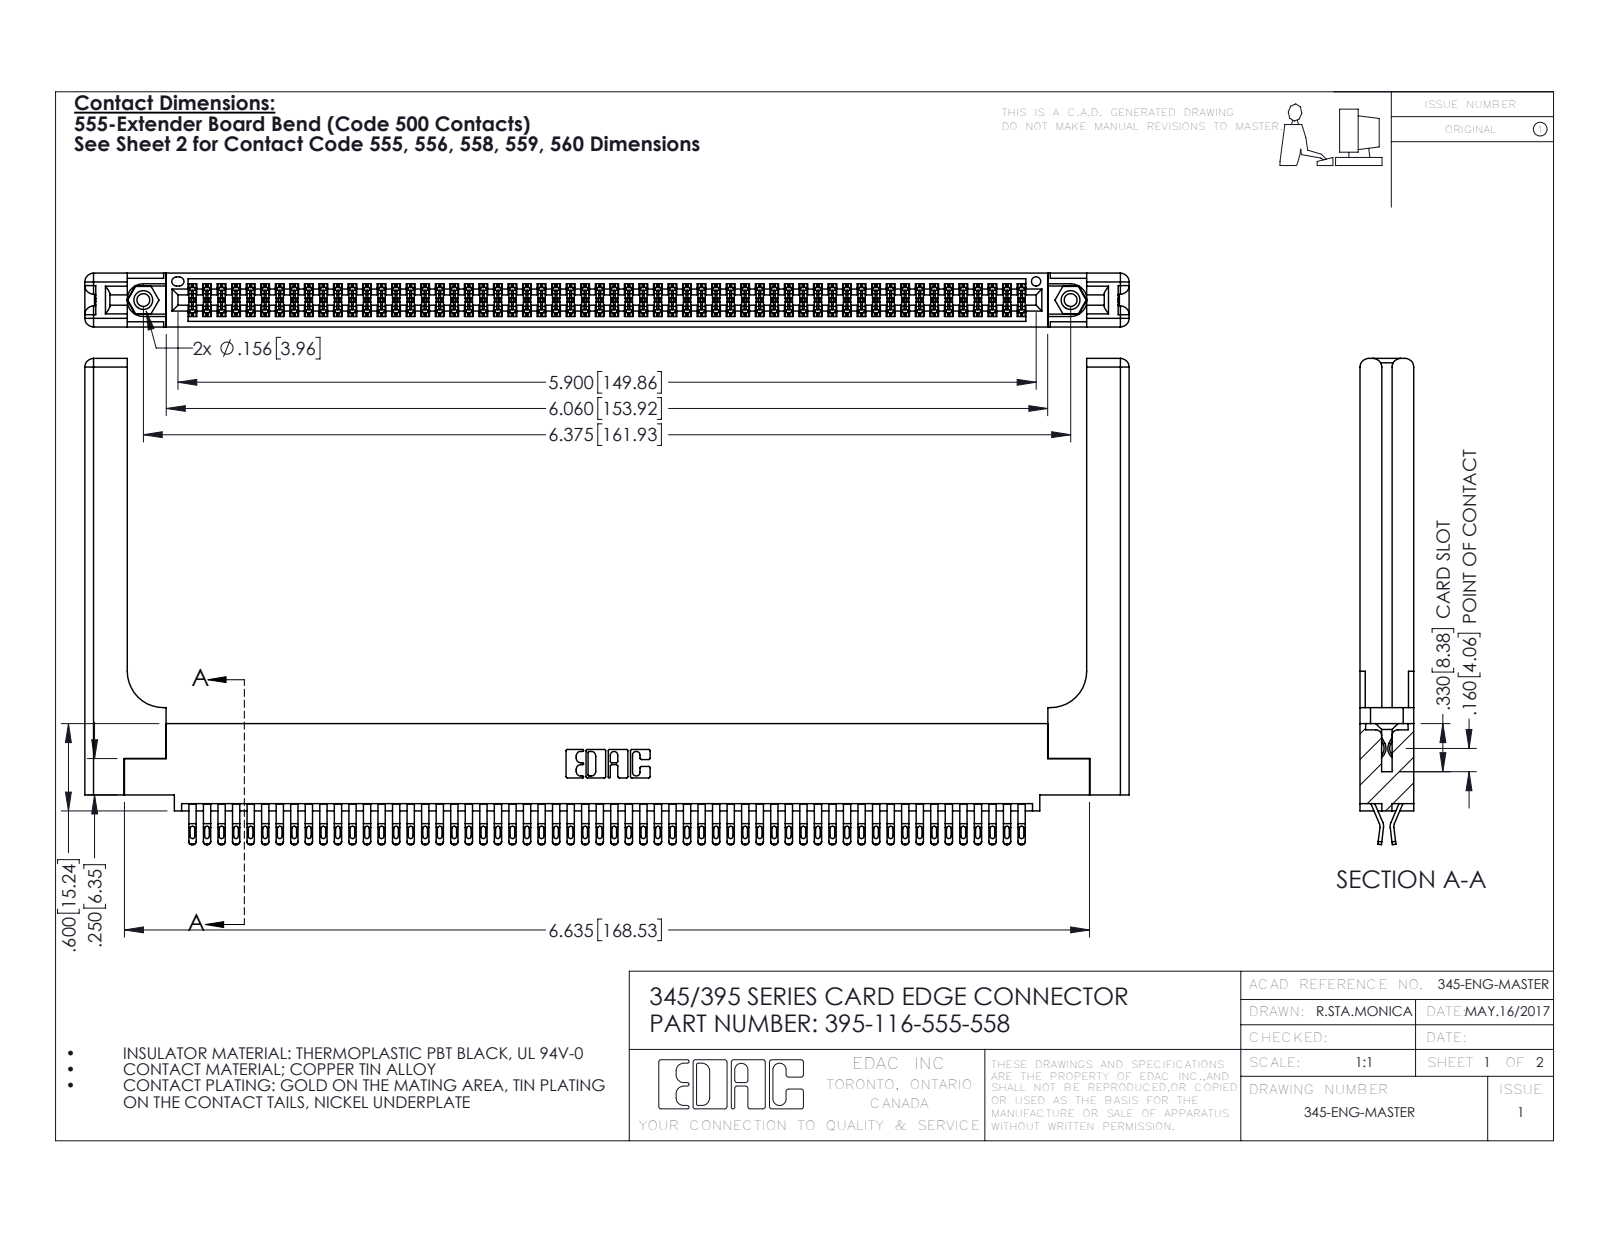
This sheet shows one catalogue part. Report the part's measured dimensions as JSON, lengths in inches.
{"part_name": "345-220-058_345-220-058; 345 Part_0.110 Offset - 0.156 Dia-TH; 345-250-001_345-250-001-102; 345-292-001_555 Tail (+1 more)", "step_written_by": "SolidWorks 2016 (CONFIG_CONTROL_DESIGN)", "units": "inches", "bodies": {"solids": 121, "faces": 6882, "planar": 3828, "cylindrical": 2994, "other": 60}, "overall_size": [7.179, 3.342, 0.37], "volume_in3": 1.623, "surface_area_in2": 51.81, "round_holes": [[0.089, 2], [0.125, 2], [0.156, 2], [0.064, 1]], "round_bosses_or_shafts": [[0.155, 2]], "partial_cylinders_radius": [[0.016, 290], [0.02, 232], [0.006, 174], [0.01, 22], [0.06, 16], [0.007, 6], [0.031, 6], [0.026, 3]], "face_to_face_distances": [0.072, 0.298, 0.37, 0.025, 0.098, 0.272, 0.2, 0.225, 0.148, 0.15], "hole_center_spacings": [0.27, 6.139, 6.375]}
